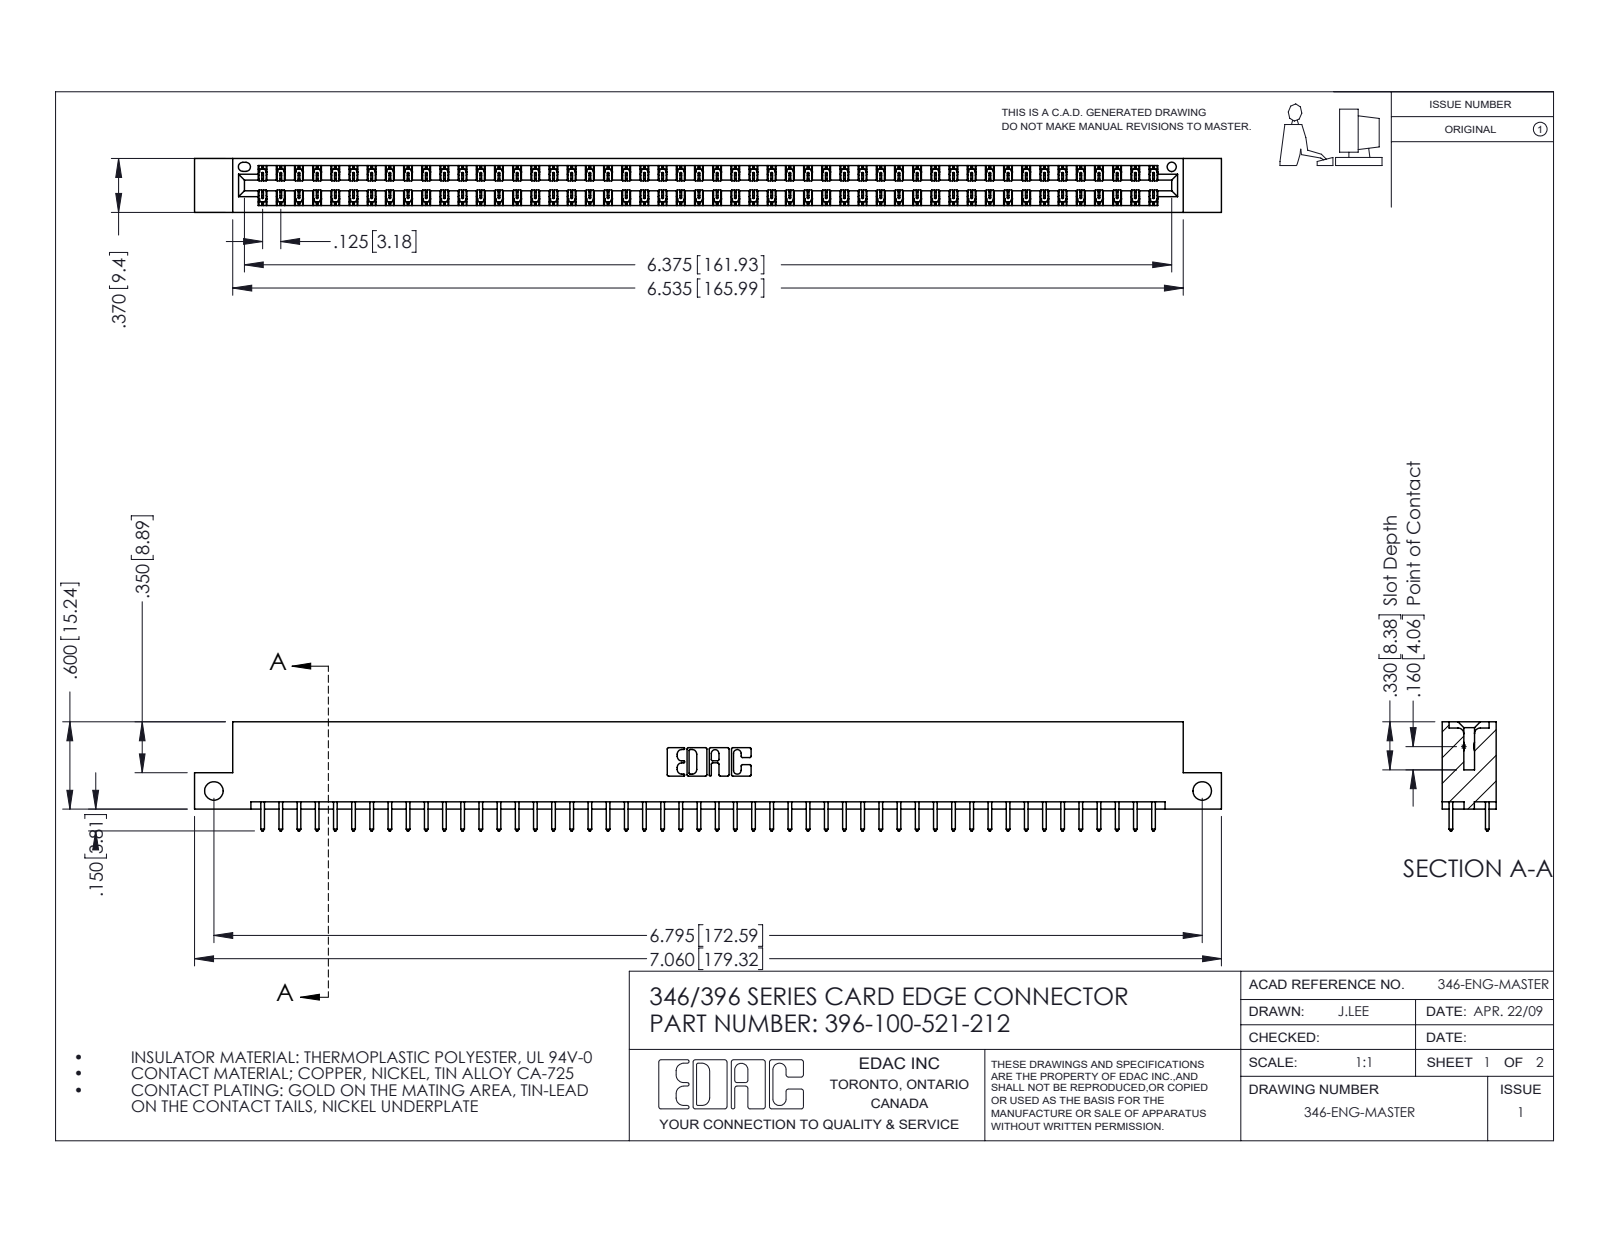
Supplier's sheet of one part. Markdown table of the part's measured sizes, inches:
| quantity | value |
| --- | --- |
| part name | 345-292-001_345-293-121; 346 Part_Flush Mounting Lugs - Side Mount; 396-100-521-212 |
| STEP written by | SolidWorks 2016 (CONFIG_CONTROL_DESIGN) |
| units | inches |
| bodies | 101 solids, 5322 faces (3576 planar, 1746 cylindrical, 0 other) |
| overall size | 7.06 × 0.75 × 0.37 |
| volume | 1.063 in³ |
| surface area | 36.67 in² |
| round holes (diameter × count) | 0.128 × 2, 0.064 × 1 |
| partial cylindrical surfaces (radius × count) | 0.006 × 150, 0.01 × 100, 0.01 × 22, 0.007 × 6, 0.031 × 6, 0.026 × 3, 0.014 × 2, 0.022 × 2 |
| main face-to-face distances | 0.048, 0.322, 0.25, 0.37, 0.072, 0.298, 0.025, 0.275, 0.148, 0.222 |
| hole center spacings | 6.795 |
